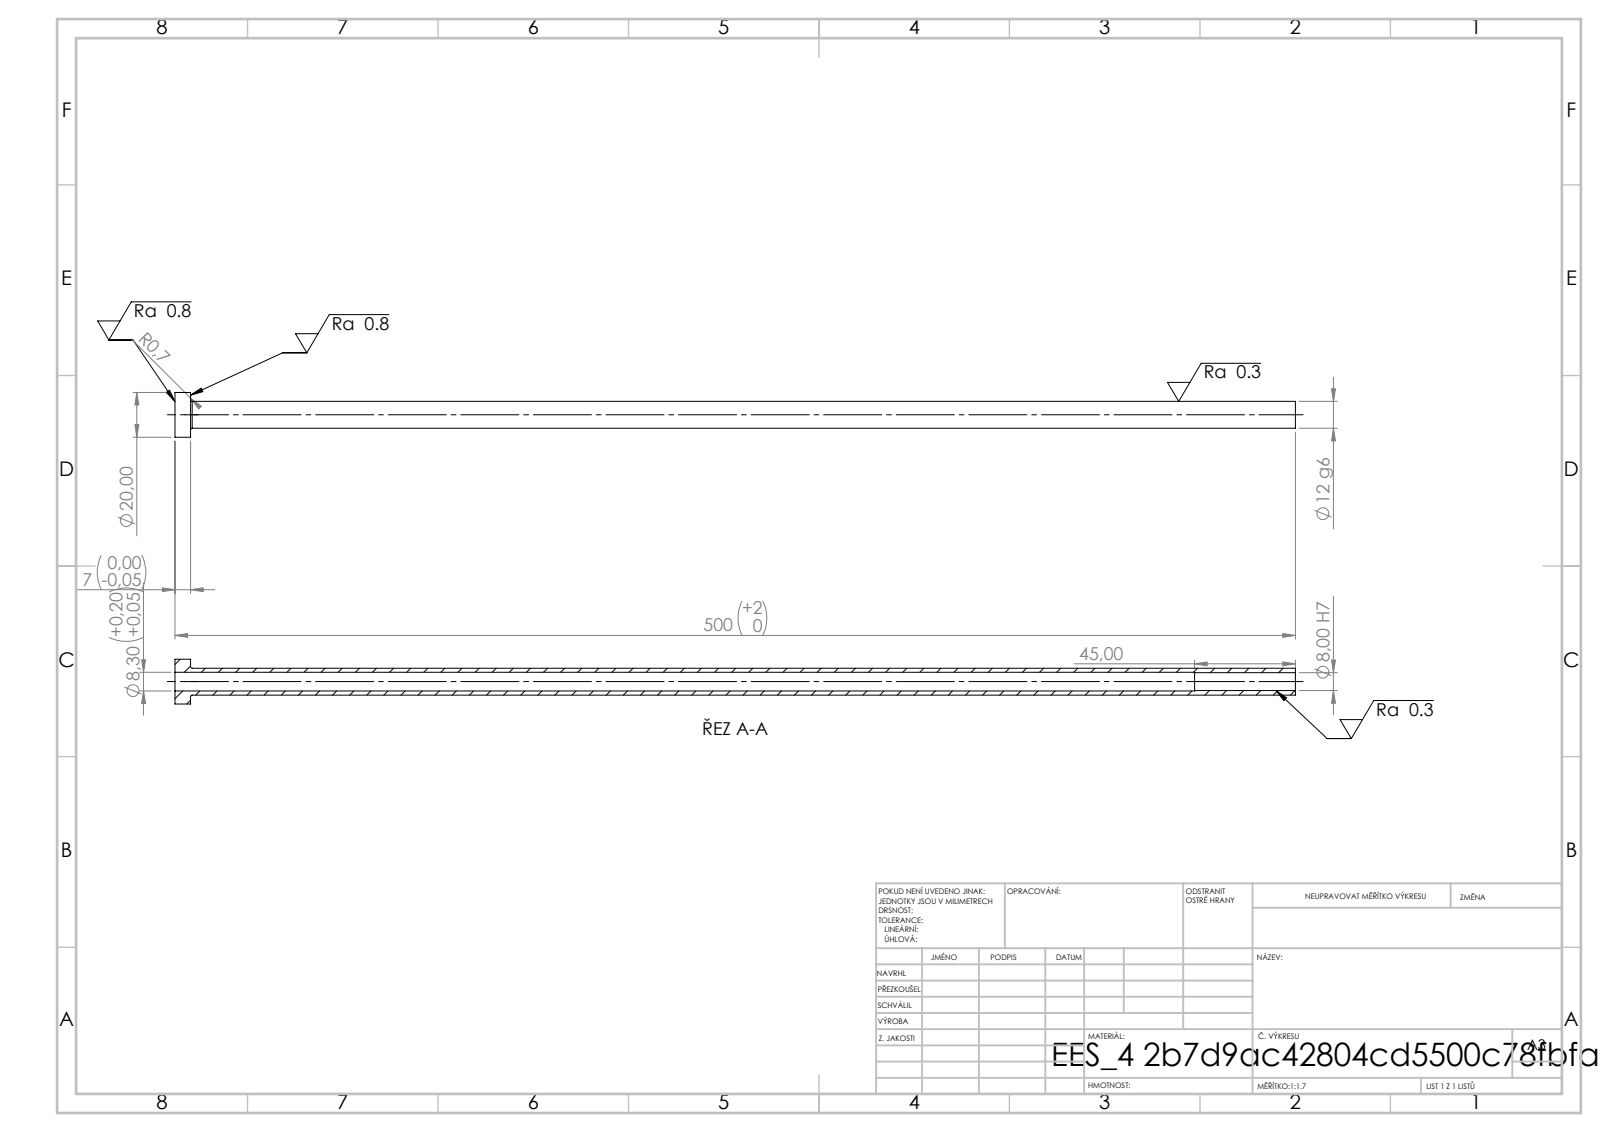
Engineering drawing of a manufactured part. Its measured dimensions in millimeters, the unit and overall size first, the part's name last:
Units: millimetres
Overall size (bounding box): 500 × 20 × 20
Round holes (diameter × count): ⌀8 ×1, ⌀8.3 ×1
Round bosses / shafts (diameter × count): ⌀20 ×1, ⌀12 ×1
Main face-to-face distances: 7, 500, 493, 455, 448, 45
Volume: 31 080 mm³ · Surface area: 32 537 mm²
Bodies: 1 solid, 14 faces (4 planar, 8 cylindrical, 2 other)
STEP written by: SolidWorks 2019 (CONFIG_CONTROL_DESIGN)
